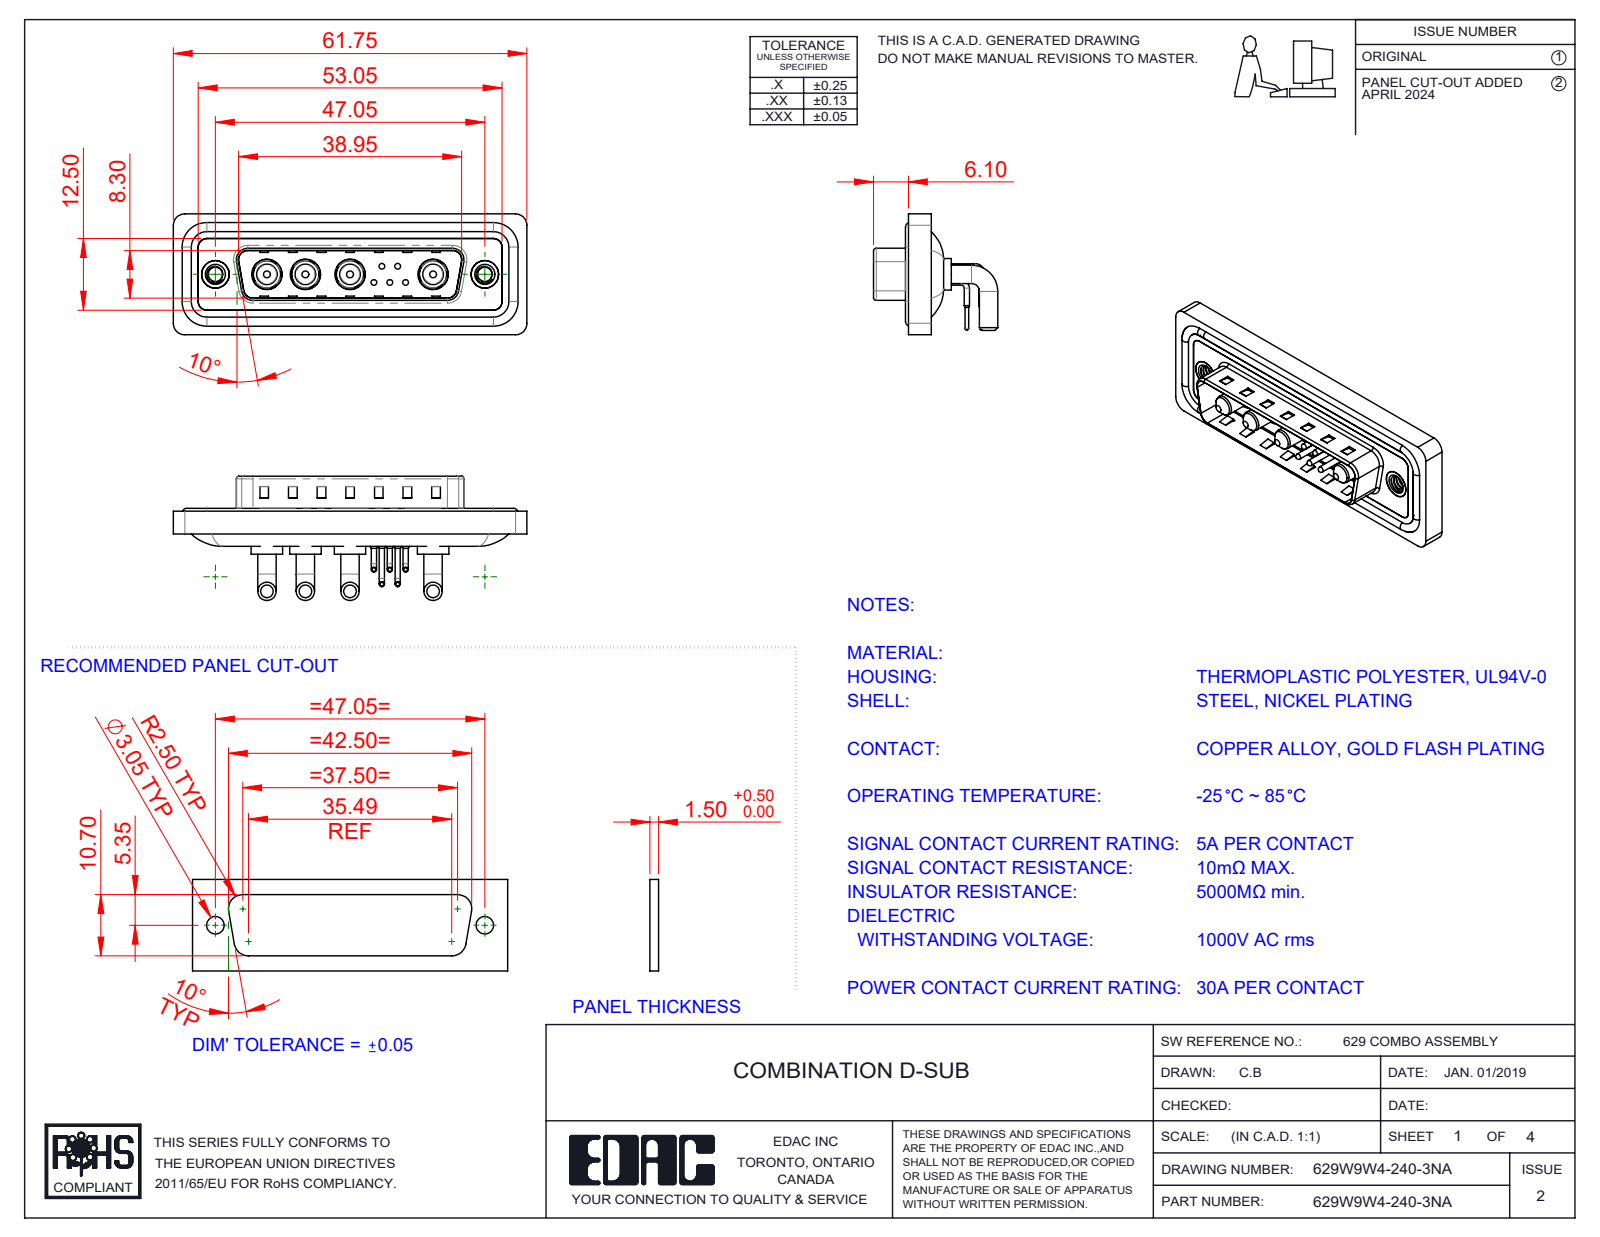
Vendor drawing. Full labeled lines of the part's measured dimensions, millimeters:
Part name (STEP PRODUCT): 629Combo Shell Front_25 Contacts; 629Combo Housing_9W4; Power Pin_30A RA; 629Combo Waterproof Housing_25 Contacts (+5 more)
STEP written by: SolidWorks 2023 (CONFIG_CONTROL_DESIGN)
Units: millimetres
Bodies: 20 solids, 1199 faces (569 planar, 450 cylindrical, 180 other)
Overall size (bounding box): 61.75 × 21.7 × 21.1
Volume: 7 820 mm³ · Surface area: 12 454 mm²
Round holes (diameter × count): ⌀0.75 ×5, ⌀1.6 ×5, ⌀2 ×5, ⌀4.85 ×4, ⌀5.3 ×4, ⌀2.5 ×2, ⌀4 ×2, ⌀4.8 ×2, ⌀5 ×2
Round bosses / shafts (diameter × count): ⌀0.9 ×10, ⌀3.2 ×8, ⌀1.5 ×5, ⌀1 ×5, ⌀0.65 ×5, ⌀5.5 ×4, ⌀5.2 ×4, ⌀4.75 ×4
Partial cylindrical surfaces — rounded edges, fillets, slot ends (radius × count): R1.5 ×18, R2 ×18, R0.5 ×8, R1.6 ×8, R1.01 ×5, R0.25 ×4, R0.6 ×4, R0.65 ×4
Main face-to-face distances: 0.4, 2.9, 0.8, 4.1, 1.1, 4.5, 2.1, 1.6, 3.1, 1.5
Hole centre spacings: 3.16, 2.77, 5.04, 14.5, 2.78, 4.4, 4.41, 5
